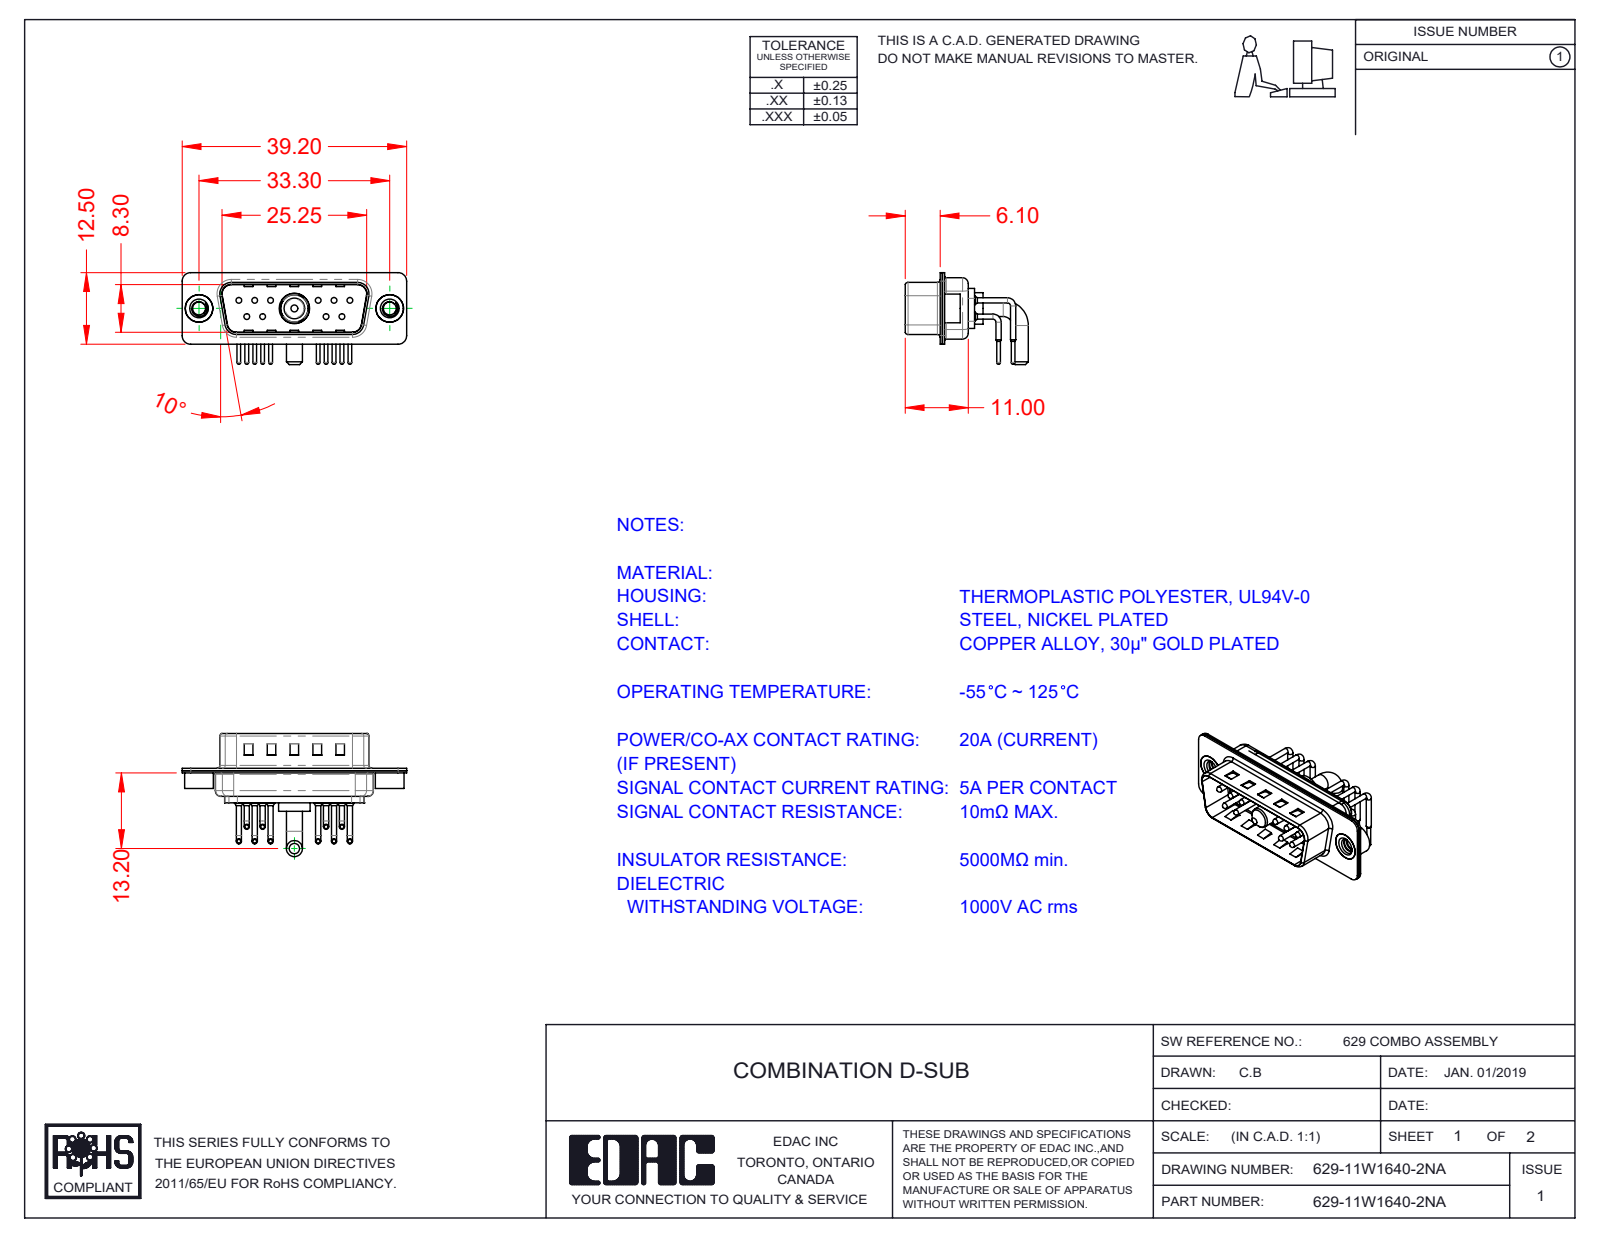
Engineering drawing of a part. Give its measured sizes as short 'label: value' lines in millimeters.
name: 629Combo Threaded Rivet_2; 629Combo Shell Rear_15 Contacts; 629Combo Contact Row 1; 629Combo Housing_11W1 (+4 more)
written by: SolidWorks 2020 (CONFIG_CONTROL_DESIGN)
unit: mm
bodies: 17 solids, 1496 faces (798 planar, 518 cylindrical, 180 other)
size: 39.2 × 21.5 × 16.05
volume: 2 064 mm³; area: 5 234 mm²
holes: 10× ⌀0.75, 10× ⌀1.6, 10× ⌀2, 2× ⌀2.26, 2× ⌀4, 2× ⌀4.8, 1× ⌀4.85, 1× ⌀5.3
bosses: 20× ⌀0.9, 10× ⌀1.5, 10× ⌀1, 10× ⌀0.65, 2× ⌀5, 2× ⌀4.9, 2× ⌀2.8, 1× ⌀5.5
rounds: 16× R1.5, 12× R2, 10× R1.01, 8× R0.5, 8× R1.6, 7× R1, 4× R0.25, 4× R0.6
face distances: 0.4, 0.8, 9.5, 9.1, 8.7, 9.9, 0.75, 5.6, 1.2, 0.35
hole spacings: 3.16, 2.77, 13.85, 11.08, 16.62, 5.03, 5.04, 5.54
